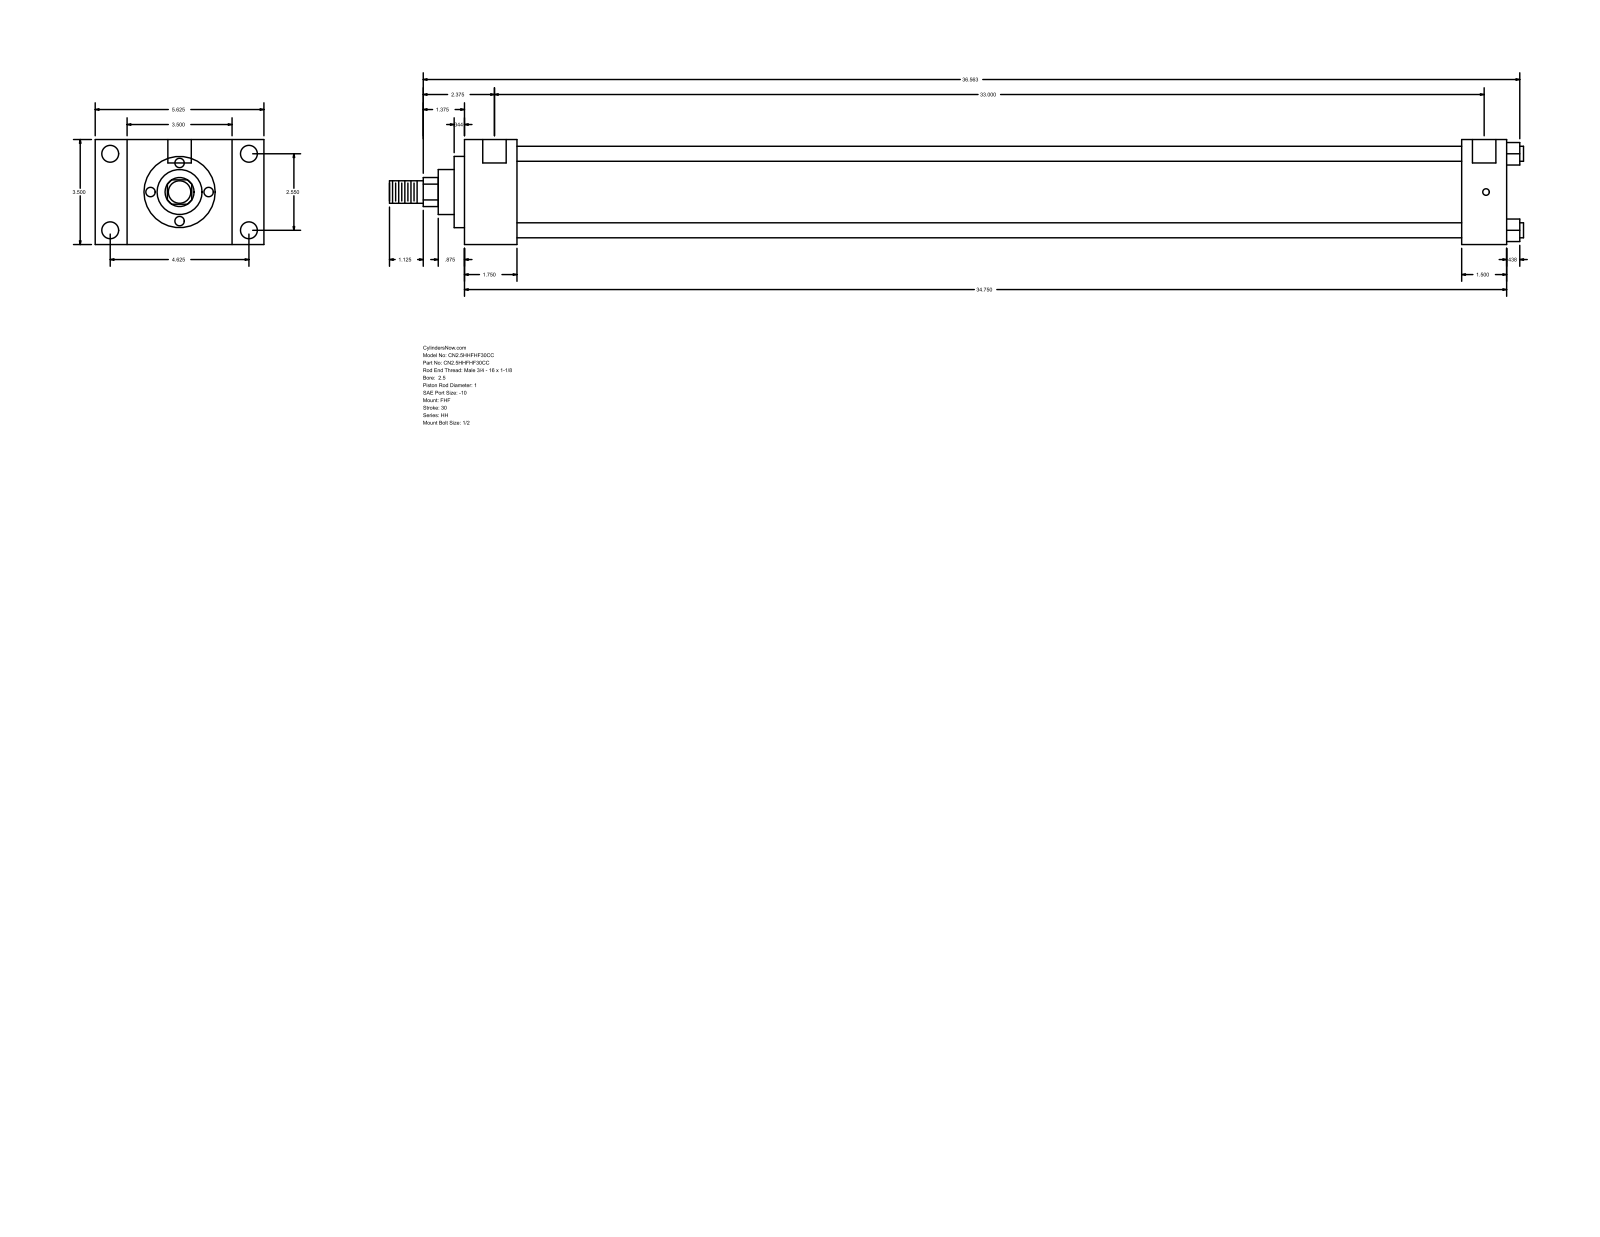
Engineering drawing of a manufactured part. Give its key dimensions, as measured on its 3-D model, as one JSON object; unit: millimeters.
{"part_name": "HH_FHF__0250_1", "step_written_by": "GSSL Pune (CONFIG_CONTROL_DESIGN)", "units": "millimeters", "bodies": {"solids": 0, "faces": 90, "planar": 61, "cylindrical": 29, "other": 0}, "overall_size": [960.44, 142.88, 88.9], "round_holes": [[5.56, 4], [14.3, 4], [19.84, 2]], "round_bosses_or_shafts": [[12.7, 4], [73.03, 1], [60.33, 1], [38.1, 1], [25.4, 1], [19.05, 1]], "partial_cylinders_radius": [[12.29, 1]], "face_to_face_distances": [88.9, 44.46, 26.99, 115.89, 882.66, 838.2, 142.88, 38.1, 844.56, 800.1], "hole_center_spacings": [1.59, 64.76, 117.48, 134.15, 839.78, 841.37, 838.19]}
